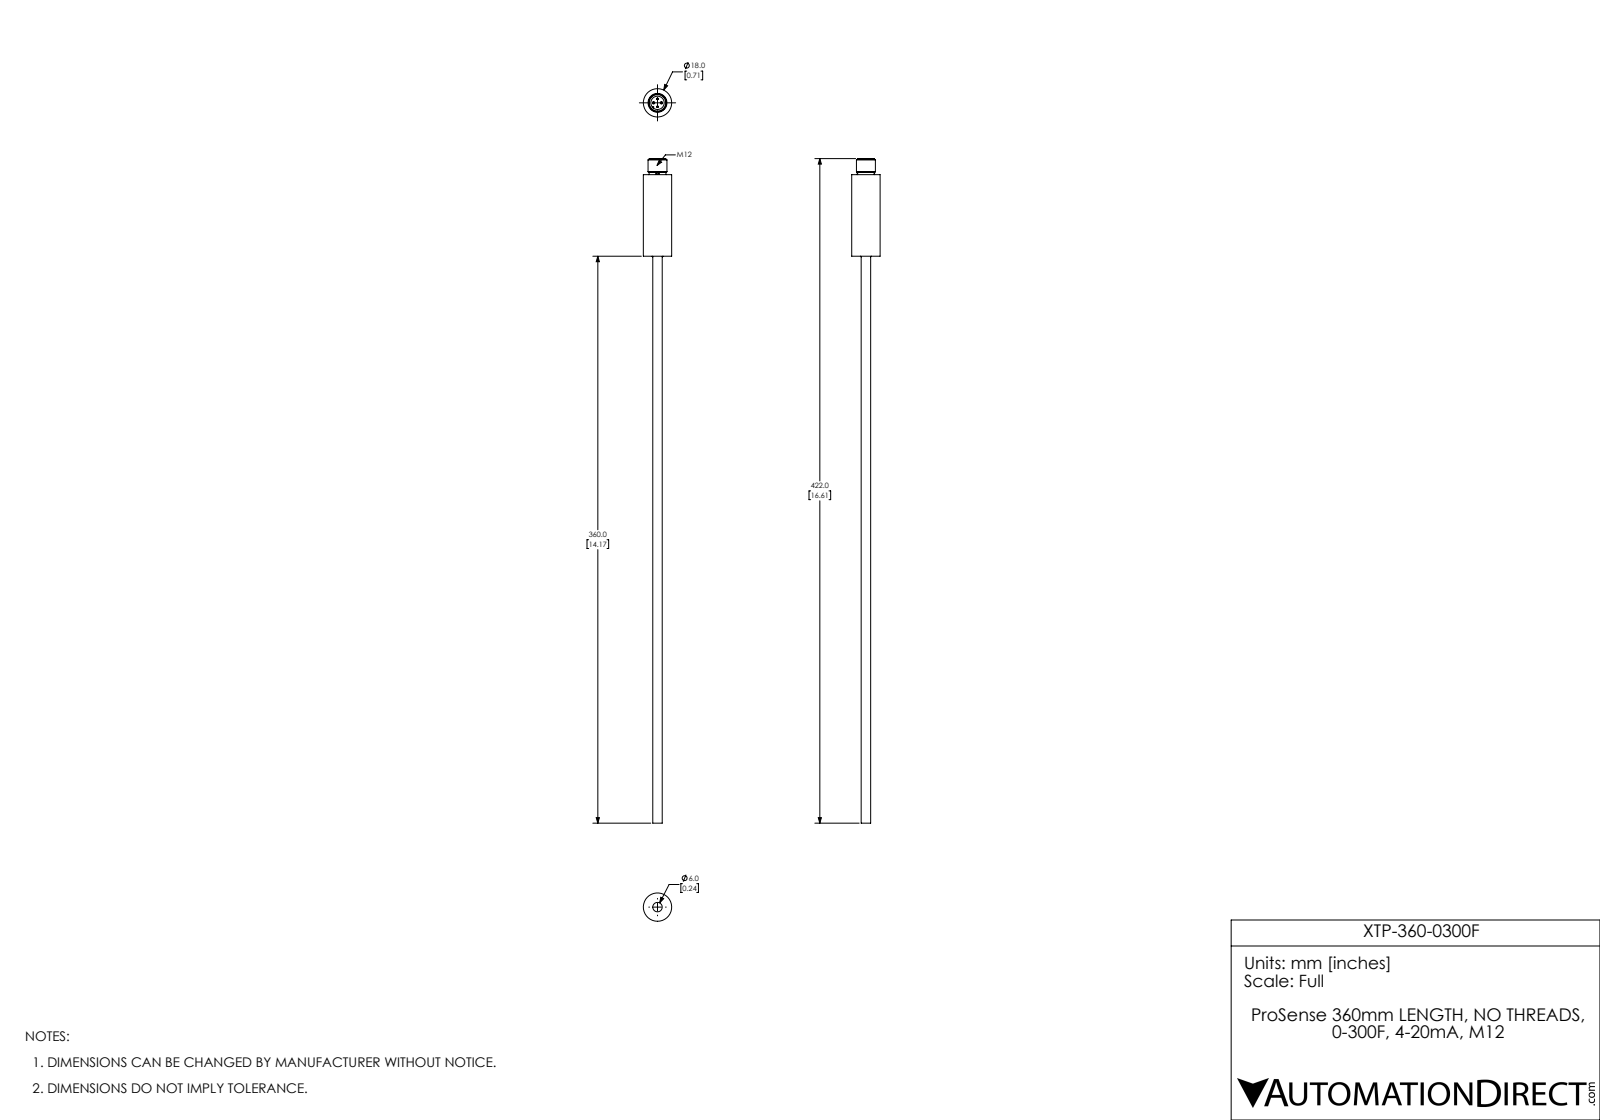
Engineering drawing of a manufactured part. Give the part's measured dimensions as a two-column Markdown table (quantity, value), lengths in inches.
| quantity | value |
| --- | --- |
| part name | XTP-360-0300F |
| STEP written by | SolidWorks 2017 (AUTOMOTIVE_DESIGN) |
| units | inches |
| bodies | 1 solid, 67 faces (24 planar, 21 cylindrical, 22 other) |
| overall size | 16.614 × 0.709 × 0.709 |
| volume | 1.463 in³ |
| surface area | 16.93 in² |
| round holes (diameter × count) | 0.335 × 1 |
| round bosses / shafts (diameter × count) | 0.04 × 4, 0.709 × 1, 0.472 × 1, 0.421 × 1, 0.413 × 1, 0.236 × 1 |
| partial cylindrical surfaces (radius × count) | 0.016 × 1 |
| main face-to-face distances | 2.039, 2.087, 0.047, 2.441, 0.402, 0.354, 14.173, 16.213, 16.26, 16.614 |
